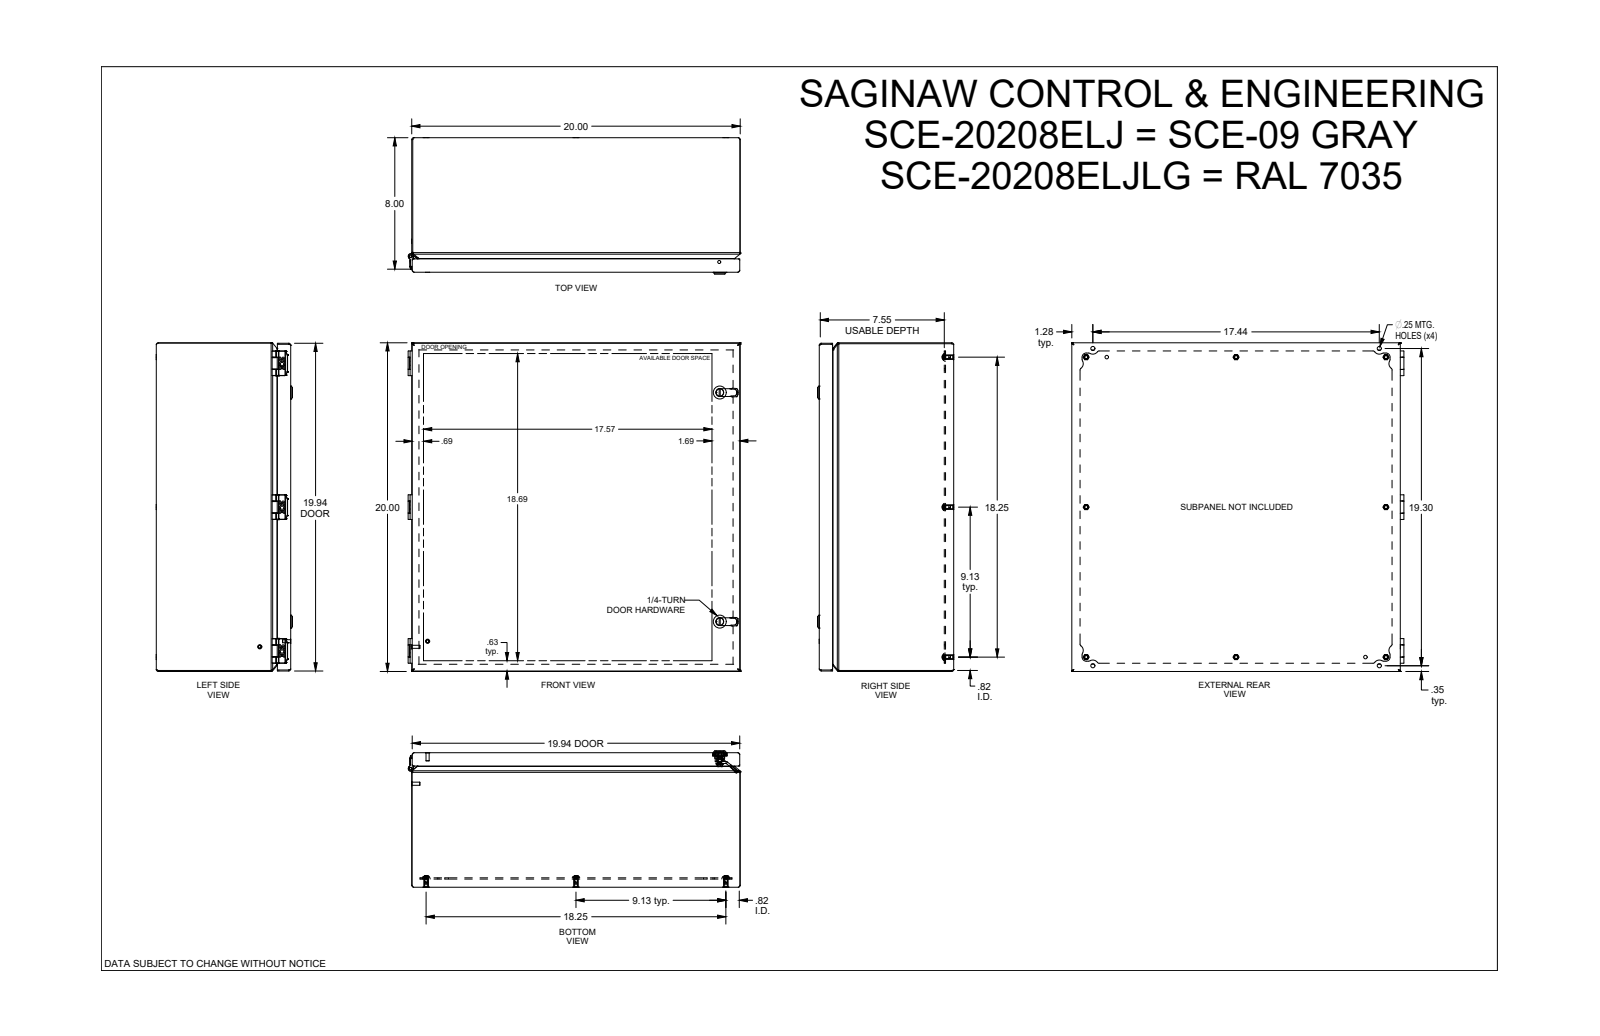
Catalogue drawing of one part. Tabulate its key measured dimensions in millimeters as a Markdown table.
| quantity | value |
| --- | --- |
| part name | SCE-20208ELJ |
| STEP written by | SolidWorks 2021 (AUTOMOTIVE_DESIGN) |
| units | millimeters |
| bodies | 36 solids, 2042 faces (647 planar, 585 cylindrical, 810 other) |
| overall size | 513.6 × 508 × 210.6 |
| volume | 1 934 000 mm³ |
| surface area | 2 426 000 mm² |
| round holes (diameter × count) | 6.4 × 12, 7.2 × 8, 4.3 × 3, 5.1 × 2, 5.5 × 2, 6.1 × 2, 6.5 × 2, 6.8 × 2, 7.2 × 2, 8.3 × 2, 12.1 × 2, 16 × 2 |
| round bosses / shafts (diameter × count) | 4.8 × 9, 9.5 × 8, 12.2 × 3, 6.6 × 3, 2.5 × 3, 0.5 × 3, 20 × 2, 13.9 × 2 |
| partial cylindrical surfaces (radius × count) | 2.7 × 99, 0.1 × 54, 0.2 × 48, 0.3 × 31, 0.3 × 18, 0.6 × 18, 1.3 × 16, 1.6 × 12 |
| main face-to-face distances | 1.5, 506.5, 1.6, 207.9, 206.4, 206.3, 204.8, 14.5, 13, 191.8 |
| hole center spacings | 231.8, 231.8, 518.3, 463.6, 221.9, 518.3, 16.9, 245.3 |
